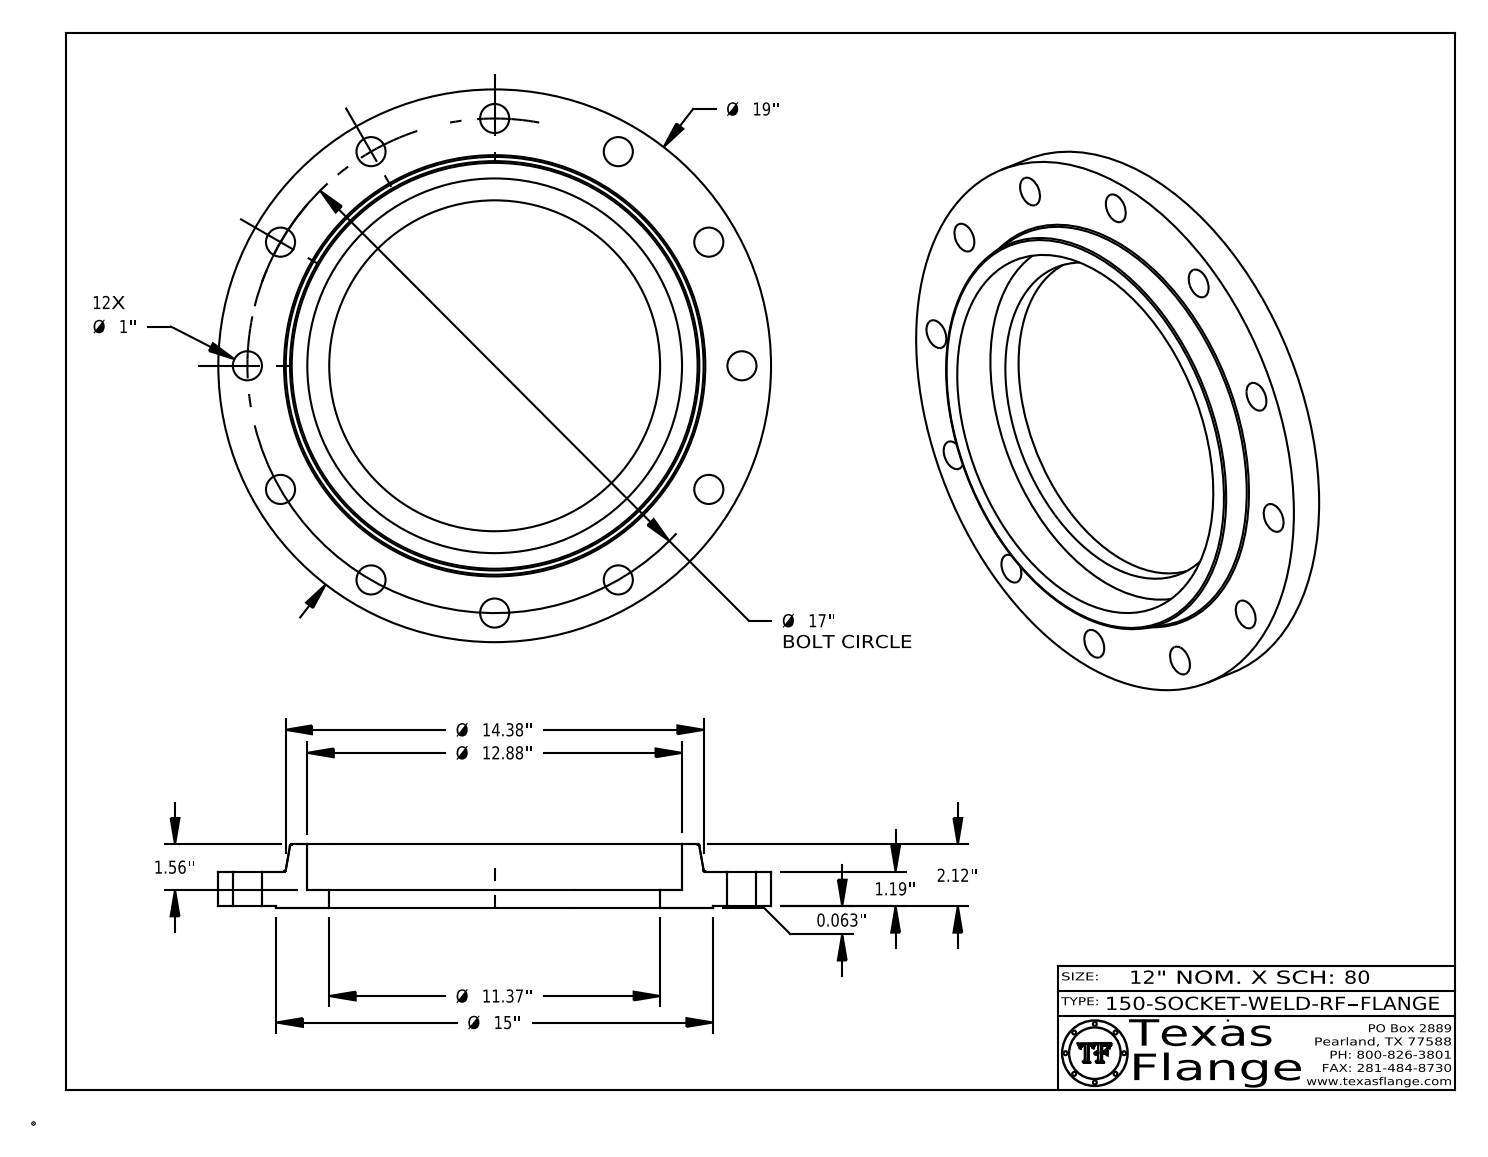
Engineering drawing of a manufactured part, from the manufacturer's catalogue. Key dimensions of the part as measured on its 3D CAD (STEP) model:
Part name (STEP PRODUCT): 150-SOCKET-WELD-RF
STEP written by: CATIA V5 STEP AP214 (AUTOMOTIVE_DESIGN)
Units: inches
Bodies: 1 solid, 428 faces (370 planar, 52 cylindrical, 6 other)
Overall size (bounding box): 19 × 19 × 2.183
Volume: 218.3 in³ · Surface area: 582.6 in²
Round holes (diameter × count): ⌀1 ×12, ⌀0.495 ×1, ⌀11.374 ×1, ⌀12.88 ×1
Round bosses / shafts (diameter × count): ⌀0.03 ×8, ⌀19 ×1, ⌀15 ×1, ⌀0.39 ×1
Main face-to-face distances: 1.19, 0.063, 1.253, 0.622, 0.56, 0.63, 2.183, 2.12, 1.56, 0.93
Hole centre spacings: 8.5, 16.42, 4.4, 12.02, 14.722, 4.4, 12.021, 14.722
